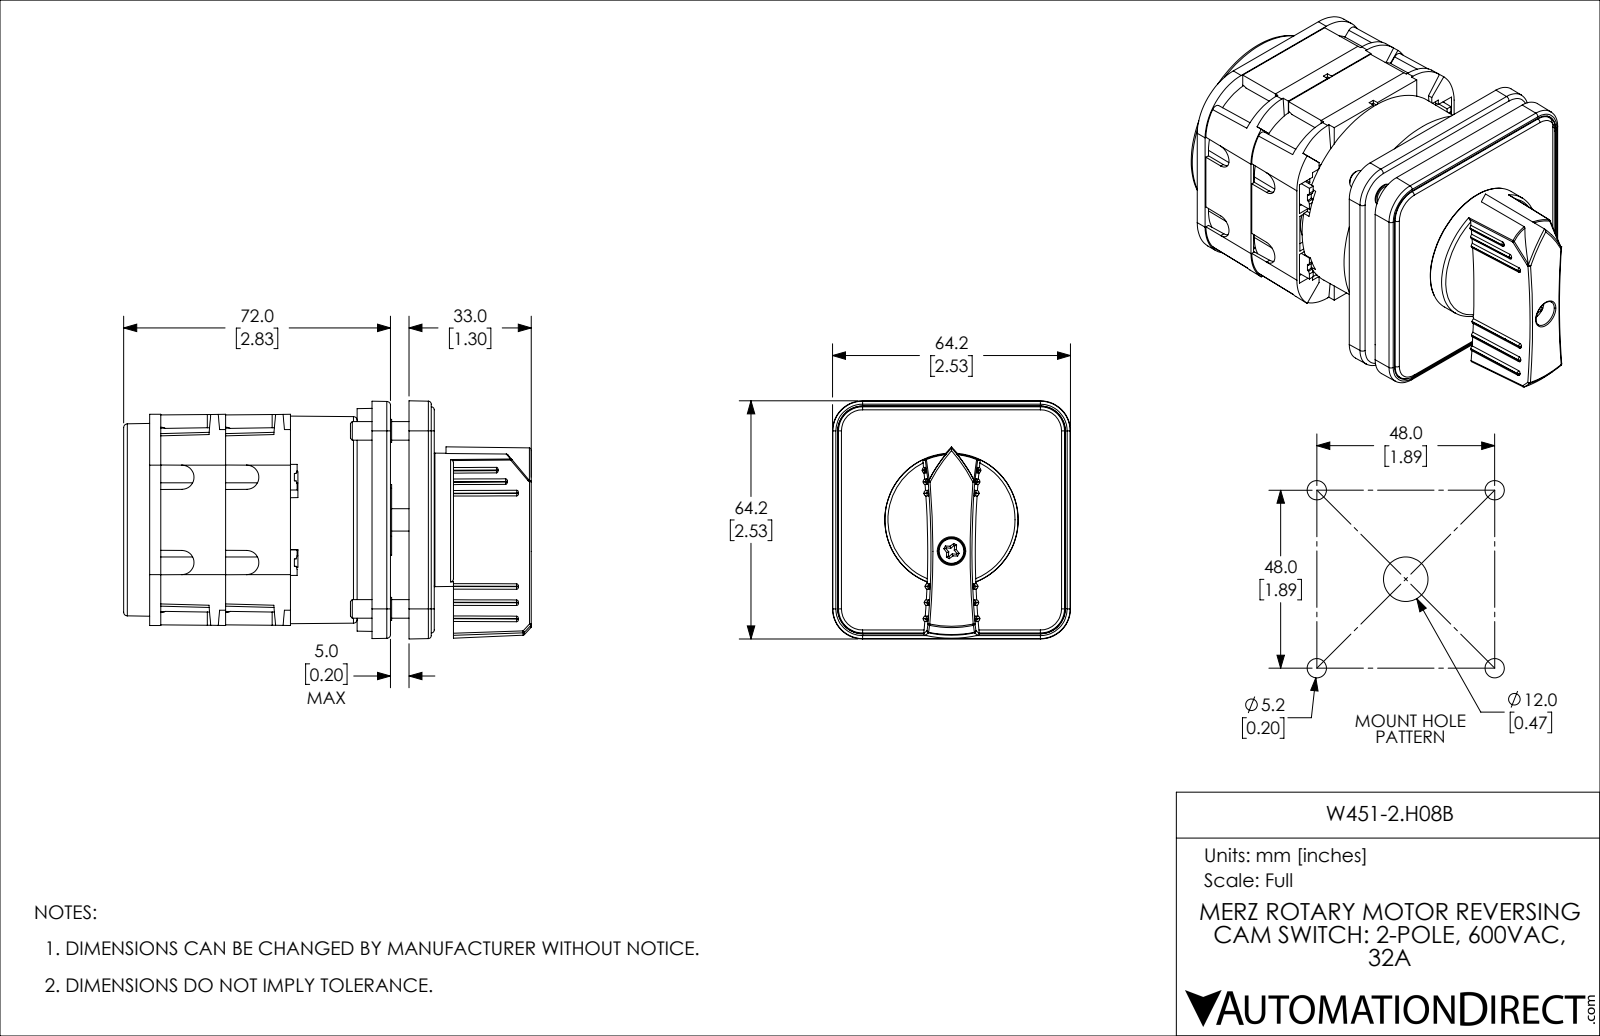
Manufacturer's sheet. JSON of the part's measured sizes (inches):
{"part_name": "W451-2.H08B", "step_written_by": "SolidWorks 2019 (AUTOMOTIVE_DESIGN)", "units": "inches", "bodies": {"solids": 12, "faces": 2897, "planar": 1679, "cylindrical": 247, "other": 971}, "overall_size": [4.331, 2.528, 2.528], "volume_in3": 12.66, "surface_area_in2": 153.3, "round_holes": [[0.315, 6], [0.012, 4], [0.157, 4], [0.197, 4], [0.205, 4], [0.374, 4], [0.24, 2], [0.394, 1], [0.512, 1], [0.551, 1], [0.925, 1]], "round_bosses_or_shafts": [[0.197, 5], [0.366, 4], [0.319, 4], [0.287, 4], [0.622, 1], [0.413, 1]], "partial_cylinders_radius": [[0.008, 14], [0.039, 13], [0.031, 11], [0.02, 6], [0.169, 6], [0.006, 4], [0.018, 4], [0.098, 4]], "face_to_face_distances": [0.098, 0.394, 0.748, 0.689, 1.457, 0.071, 0.465, 0.717, 0.197, 0.591], "hole_center_spacings": [0.802, 1.67, 0.334, 0.355, 0.368, 0.374, 0.644, 0.648]}
